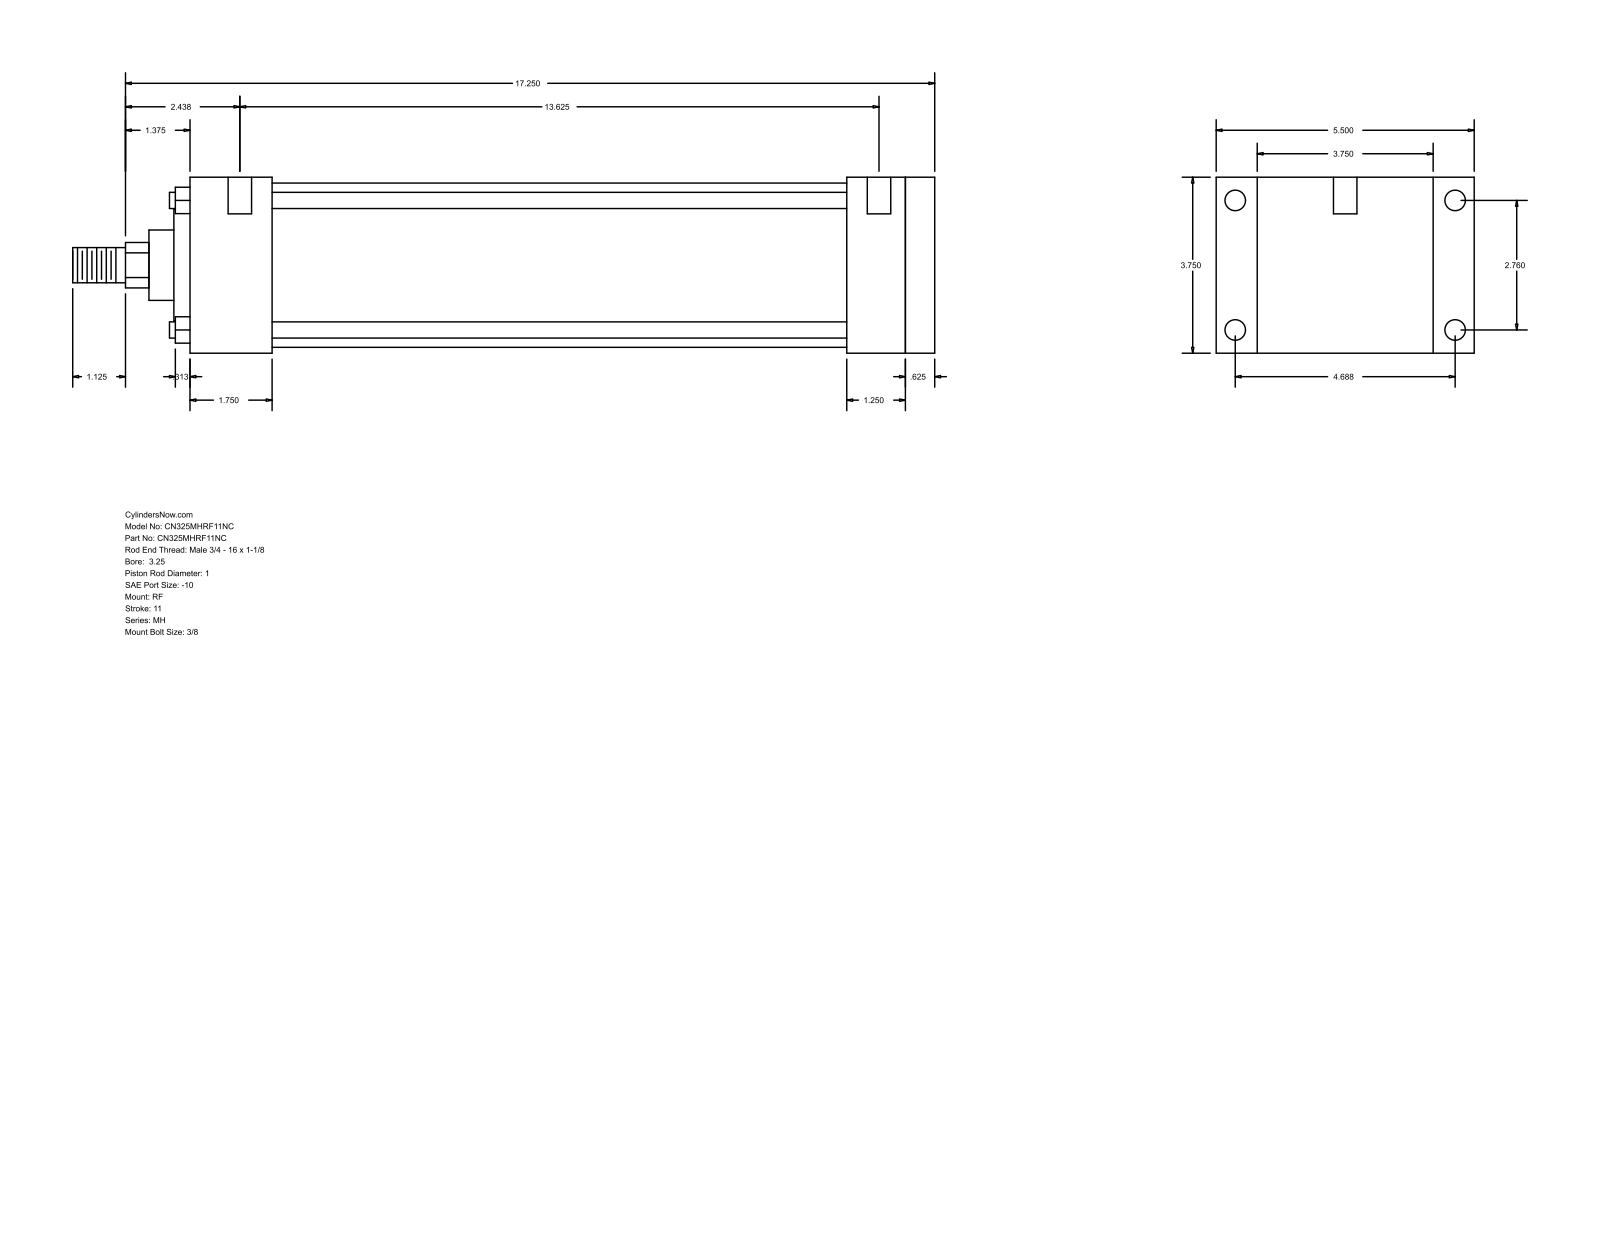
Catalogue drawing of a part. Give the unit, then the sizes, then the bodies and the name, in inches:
Units: inches
Overall size (bounding box): 18.375 × 5.5 × 3.75
Round holes (diameter × count): ⌀0.219 ×4, ⌀0.438 ×4, ⌀0.5 ×2
Round bosses / shafts (diameter × count): ⌀0.345 ×4, ⌀3.5 ×1, ⌀2.375 ×1, ⌀1.5 ×1, ⌀1 ×1, ⌀0.75 ×1
Partial cylindrical surfaces — rounded edges, fillets, slot ends (radius × count): R0.484 ×1
Main face-to-face distances: 3.75, 15.875, 15.25, 0.625, 0.875, 4.625, 1.75, 13.5, 14.125, 14
Hole centre spacings: 2.76, 4.687, 5.439, 13.875, 0.062, 0.187, 13.625, 13.687
Bodies: 0 solids, 94 faces (65 planar, 29 cylindrical, 0 other)
Part name (STEP PRODUCT): MH_RF__0325_1
STEP written by: GSSL Pune (CONFIG_CONTROL_DESIGN)
